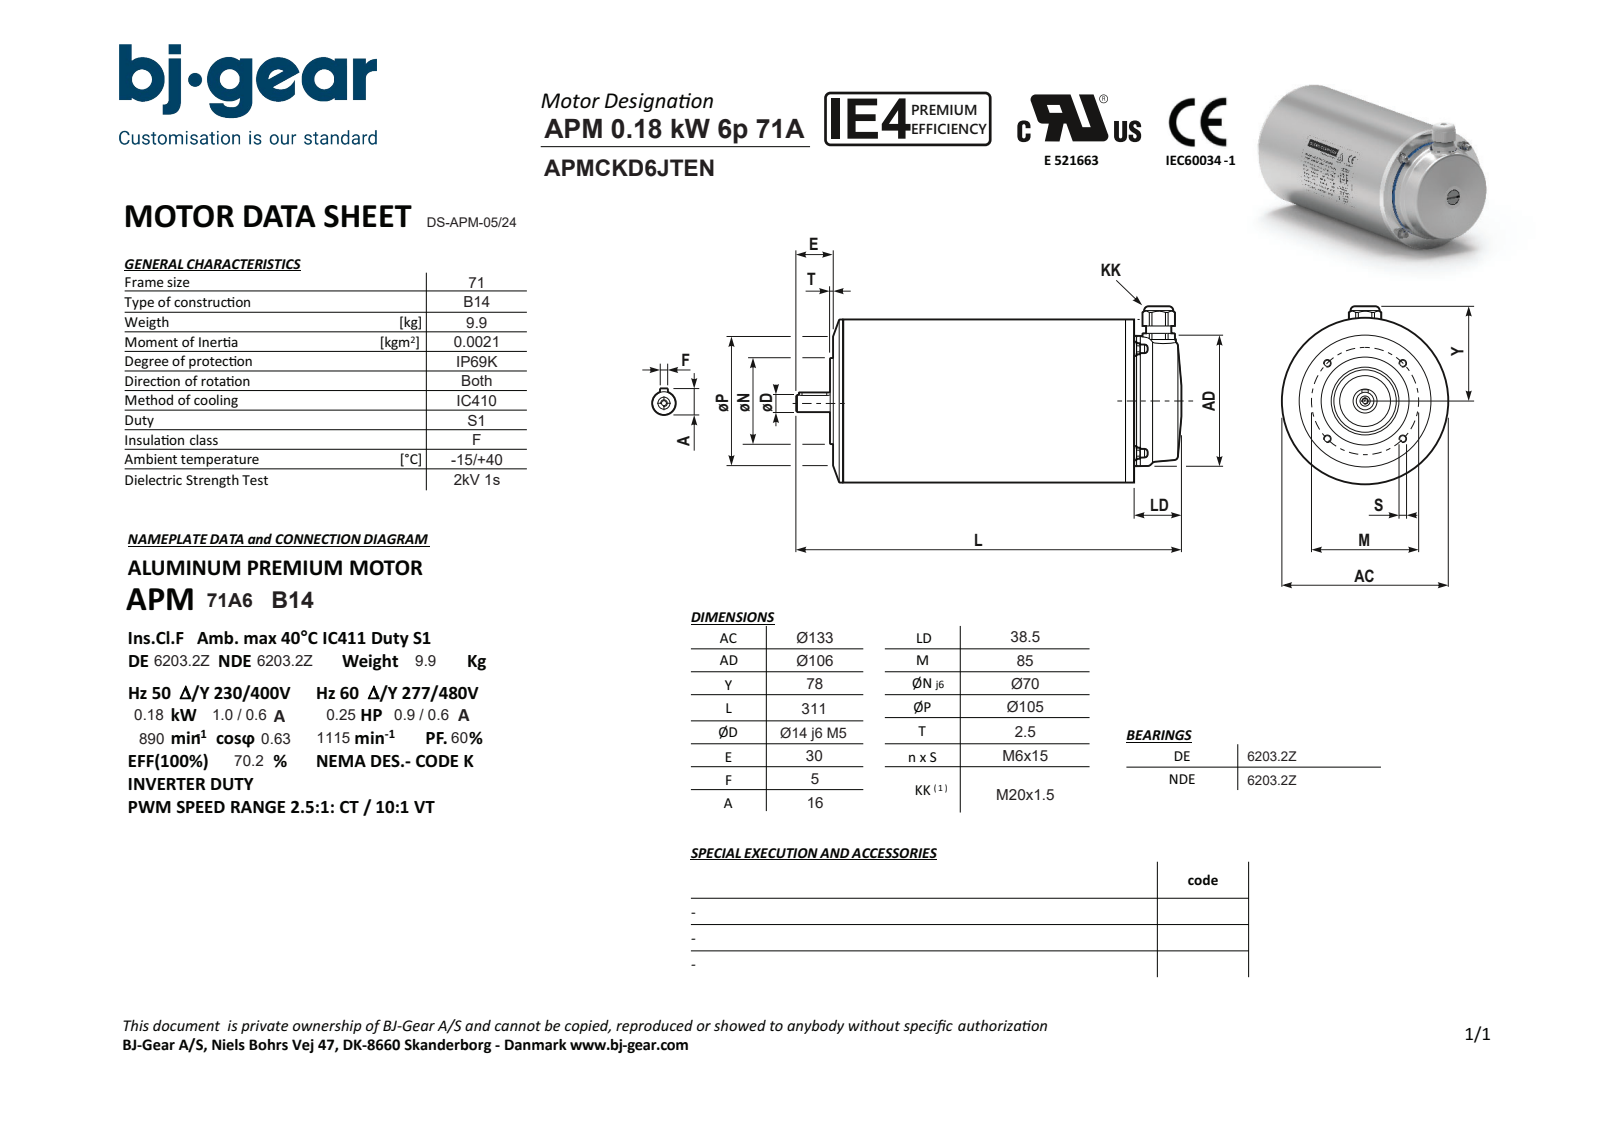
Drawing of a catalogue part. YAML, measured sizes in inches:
part_name: "APMCKD6JTENN4KCR2-N---NNN"
step_written_by: "Solid Edge (AUTOMOTIVE_DESIGN)"
units: inches
bodies: {solids: 1, faces: 156, planar: 71, cylindrical: 50, other: 35}
overall_size: [12.244, 5.642, 5.22]
volume: 222.1
surface_area: 225
round_holes:
  - {diameter: 0.194, count: 4}
  - {diameter: 0.163, count: 1}
  - {diameter: 0.209, count: 1}
  - {diameter: 0.63, count: 1}
  - {diameter: 1.102, count: 1}
  - {diameter: 2.047, count: 1}
round_bosses_or_shafts:
  - {diameter: 0.453, count: 4}
  - {diameter: 0.276, count: 4}
  - {diameter: 5.22, count: 1}
  - {diameter: 5.22, count: 1}
  - {diameter: 4.173, count: 1}
  - {diameter: 2.756, count: 1}
  - {diameter: 0.933, count: 1}
  - {diameter: 0.811, count: 1}
partial_cylinders:
  - {radius: 0.098, count: 2}
  - {radius: 0.52, count: 1}
face_to_face_distances: [9.547, 9.331, 0.217, 0.315, 0.098, 9.646, 11.161, 1.516, 10.846, 11.063]
hole_center_spacings: [1.673, 2.366, 3.346]
